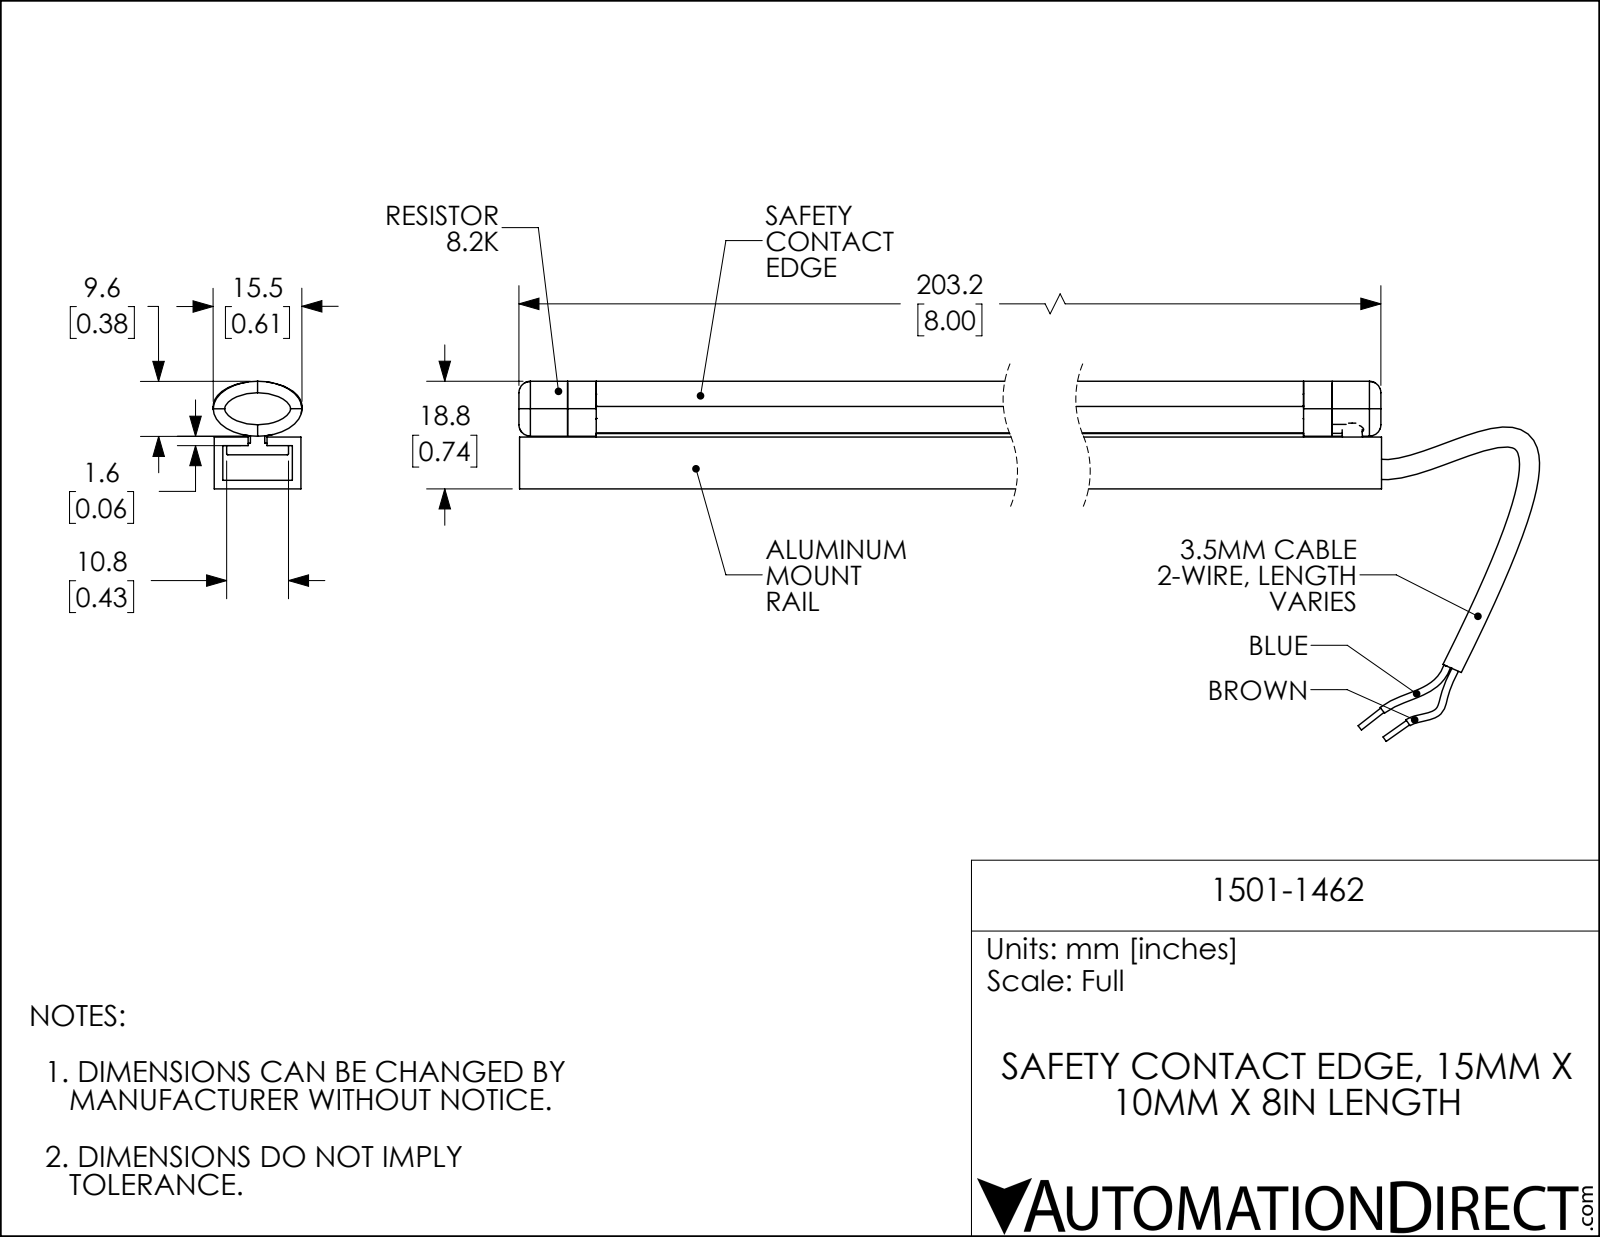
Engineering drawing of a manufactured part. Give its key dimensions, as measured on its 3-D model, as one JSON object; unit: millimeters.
{"part_name": "1501-1462", "step_written_by": "SolidWorks 2018 (AUTOMOTIVE_DESIGN)", "units": "millimeters", "bodies": {"solids": 7, "faces": 607, "planar": 129, "cylindrical": 154, "other": 324}, "overall_size": [230.9, 62.9, 15.5], "volume_mm3": 33170, "surface_area_mm2": 38030, "round_holes": [[1.2, 4]], "round_bosses_or_shafts": [[0.9, 2]], "partial_cylinders_radius": [[0.1, 52], [0.4, 15], [0.3, 10], [0.2, 7], [0.5, 4], [13, 4], [0.2, 3], [1.5, 3]], "face_to_face_distances": [1.5, 7.5, 13.6, 9, 0.4, 3.1, 15.1, 5.9, 4.4, 6], "hole_center_spacings": [5, 5, 5]}
